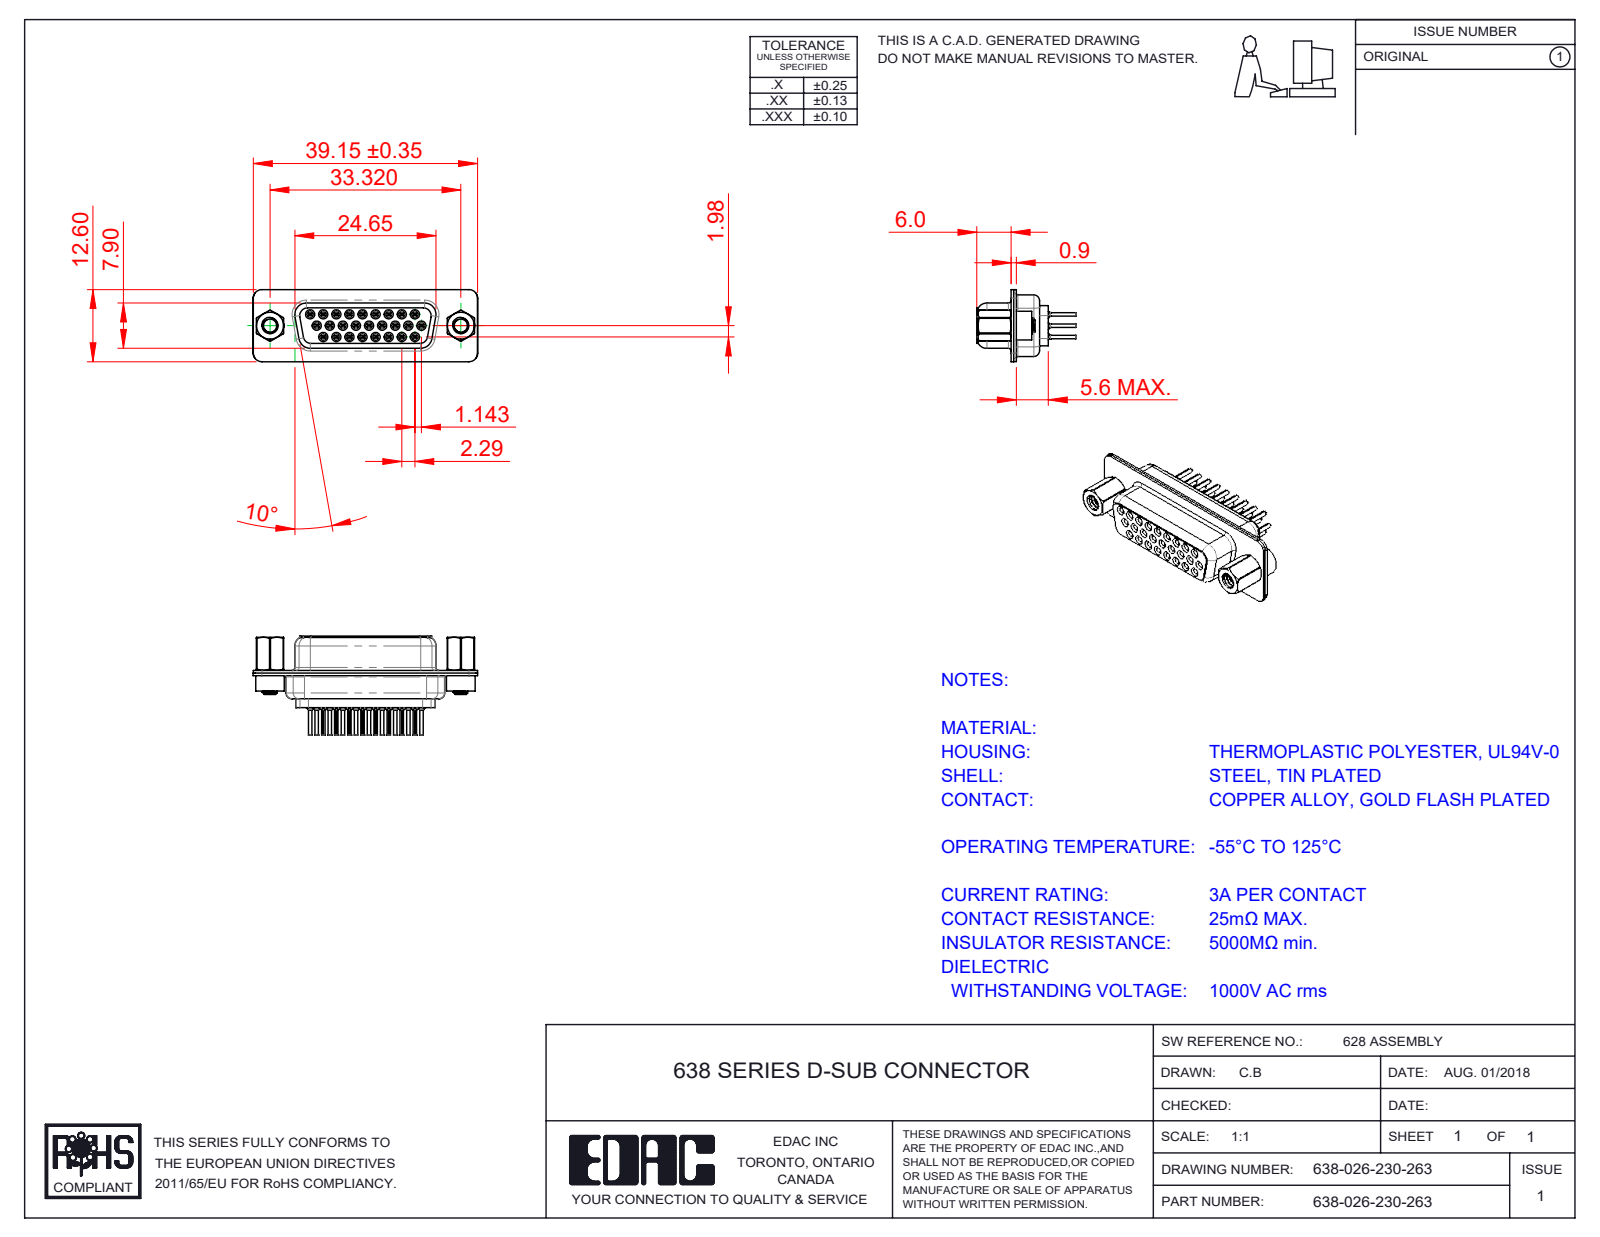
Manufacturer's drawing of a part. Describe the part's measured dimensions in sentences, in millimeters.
The part is named "638-026-230-263; 638 Housing_26 Contacts; 638 Shell Rear_26 Contacts; 638 4-40 Hex Standoff (+5 more)". Its 3-D file was written by "SolidWorks 2020 (CONFIG_CONTROL_DESIGN)". It is 33 solids with 3707 faces: 895 planar, 1067 cylindrical and 1745 other. Overall it measures 39.19 by 17.3 by 12.6 millimeters. Its volume is 2 426 cubic millimeters and its surface area 8 790 square millimeters. Round holes: 26 of diameter 0.2, 26 of diameter 0.8, 26 of diameter 1, 26 of diameter 1.1, 26 of diameter 1.6, 26 of diameter 1.7, 26 of diameter 1.8, 2 of diameter 2.26, 2 of diameter 2.29, 2 of diameter 4, 2 of diameter 4.05, 2 of diameter 4.85. Round bosses or shafts: 26 of diameter 2, 26 of diameter 1.5, 26 of diameter 1.2, 26 of diameter 0.6, 2 of diameter 5, 2 of diameter 4.95, 2 of diameter 4.8, 2 of diameter 2.79. Partial cylindrical surfaces (rounded edges, fillets, slot ends): 52 of radius 0.1, 20 of radius 1.5, 18 of radius 0.28, 12 of radius 2, 8 of radius 1.55, 5 of radius 1.35, 4 of radius 0.25, 4 of radius 0.5. The main face-to-face distances are 0.45, 0.4, 0.9, 1.43, 8.88, 6.6, 2.28, 1.4, 0.85, 6.2. The hole center spacings are 3.96, 2.28, 4.57, 6.05, 2.29, 8.24, 6.86, 10.48.
